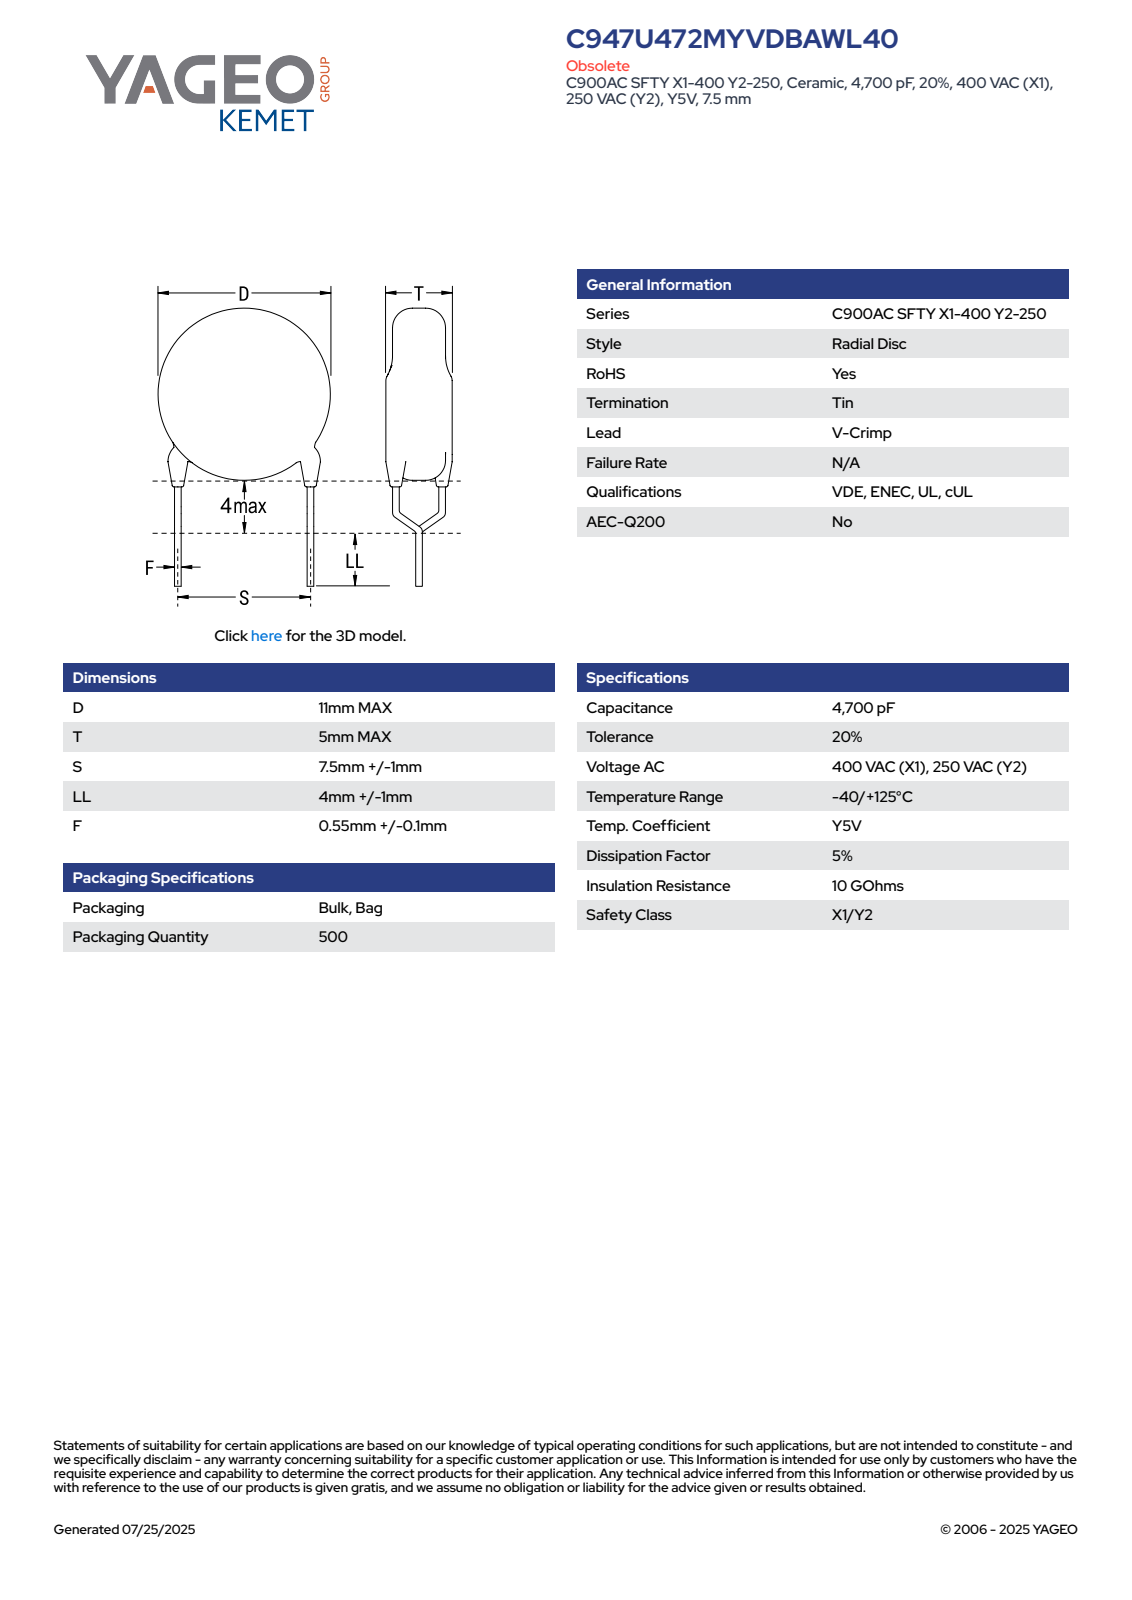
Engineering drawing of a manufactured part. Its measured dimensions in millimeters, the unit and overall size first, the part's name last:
Units: millimetres
Overall size (bounding box): 19.8 × 11 × 5
Round bosses / shafts (diameter × count): ⌀0.65 ×6, ⌀11 ×1
Main face-to-face distances: 5, 7.9, 15.01, 7.11, 13.58, 5.68, 1.43, 0.39, 0.35, 5.84
Volume: 469 mm³ · Surface area: 390 mm²
Bodies: 5 solids, 93 faces (65 planar, 16 cylindrical, 12 other)
Part name (STEP PRODUCT): CCD_VCC900_D11T5S7.5LL5F0.65
STEP written by: SolidWorks 2014 (AUTOMOTIVE_DESIGN)
